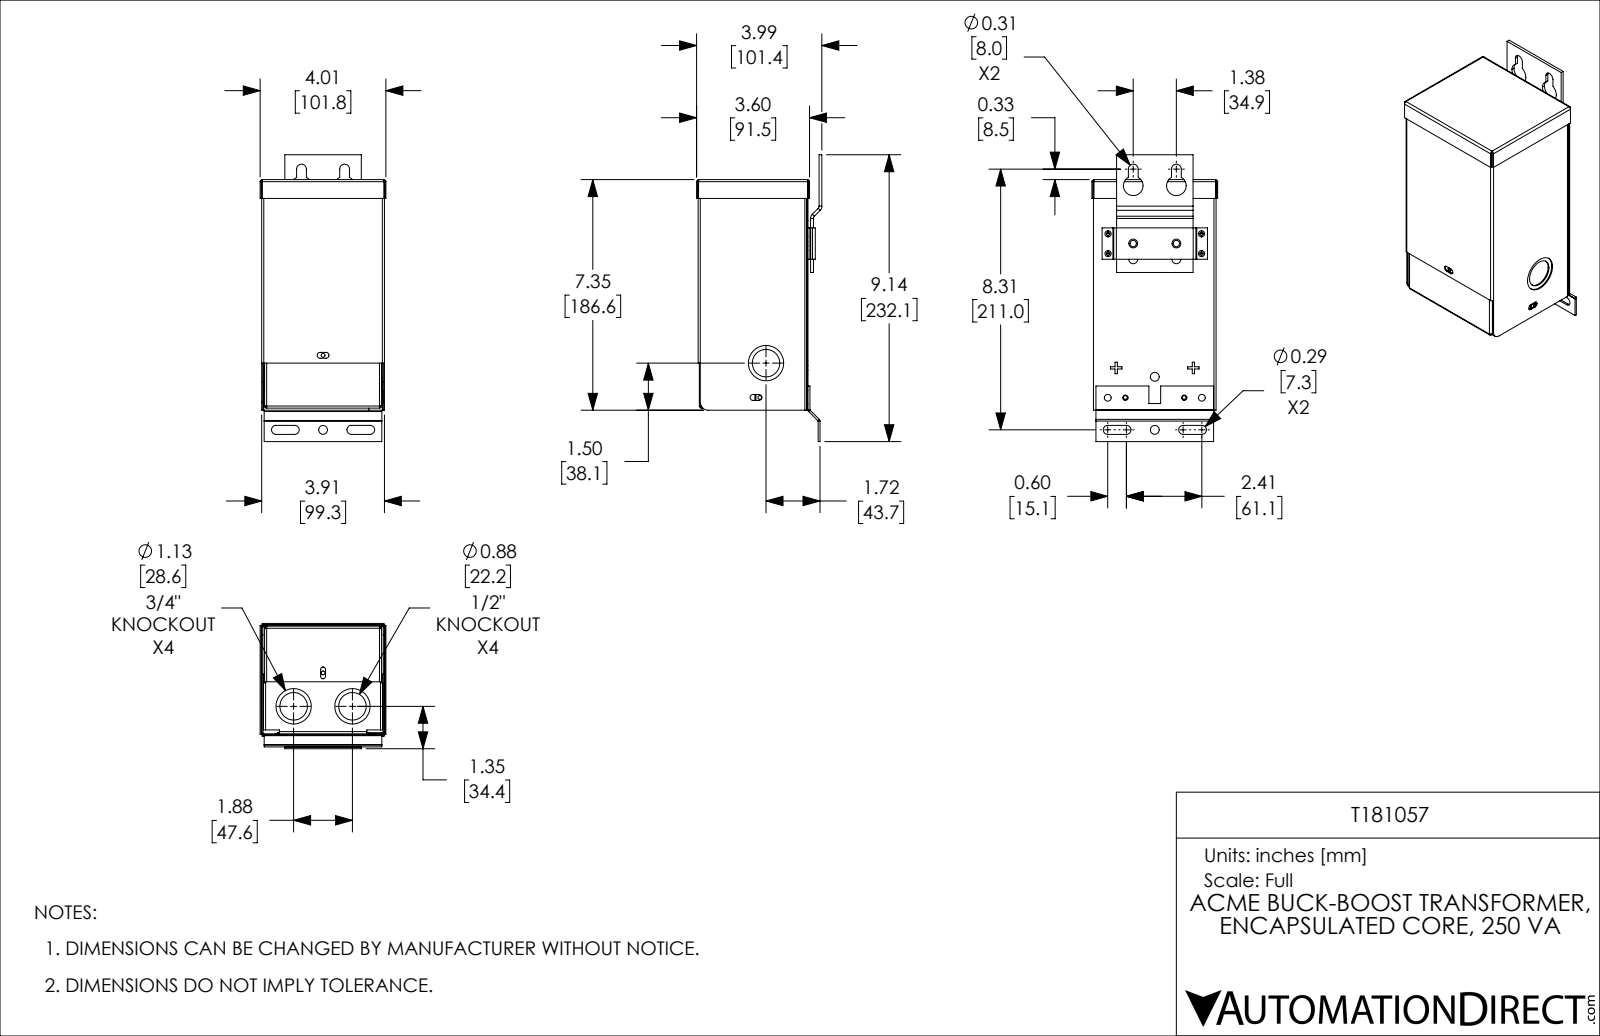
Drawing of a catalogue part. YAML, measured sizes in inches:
part_name: "T181057"
step_written_by: "SolidWorks 2021 (CONFIG_CONTROL_DESIGN)"
units: inches
bodies: {solids: 7, faces: 528, planar: 326, cylindrical: 154, other: 48}
overall_size: [9.137, 4.008, 3.993]
volume: 6.9
surface_area: 352.5
round_holes:
  - {diameter: 0.12, count: 5}
  - {diameter: 0.281, count: 3}
  - {diameter: 0.281, count: 3}
  - {diameter: 0.875, count: 3}
  - {diameter: 1.125, count: 3}
  - {diameter: 0.171, count: 2}
  - {diameter: 0.187, count: 2}
  - {diameter: 0.201, count: 2}
  - {diameter: 0.218, count: 2}
  - {diameter: 0.625, count: 2}
  - {diameter: 1.125, count: 1}
round_bosses_or_shafts:
  - {diameter: 1.197, count: 3}
  - {diameter: 0.947, count: 3}
partial_cylinders:
  - {radius: 0.031, count: 16}
  - {radius: 0.067, count: 16}
  - {radius: 0.094, count: 8}
  - {radius: 0.026, count: 4}
  - {radius: 0.086, count: 4}
  - {radius: 0.144, count: 4}
  - {radius: 0.017, count: 2}
  - {radius: 0.077, count: 2}
face_to_face_distances: [0.036, 3.464, 3.874, 3.428, 3.91, 3.839, 3.5, 0.06, 7.242, 7.182]
hole_center_spacings: [1.375, 0.5, 0.502, 0.562, 0.563, 1.145, 1.151, 1.376]
